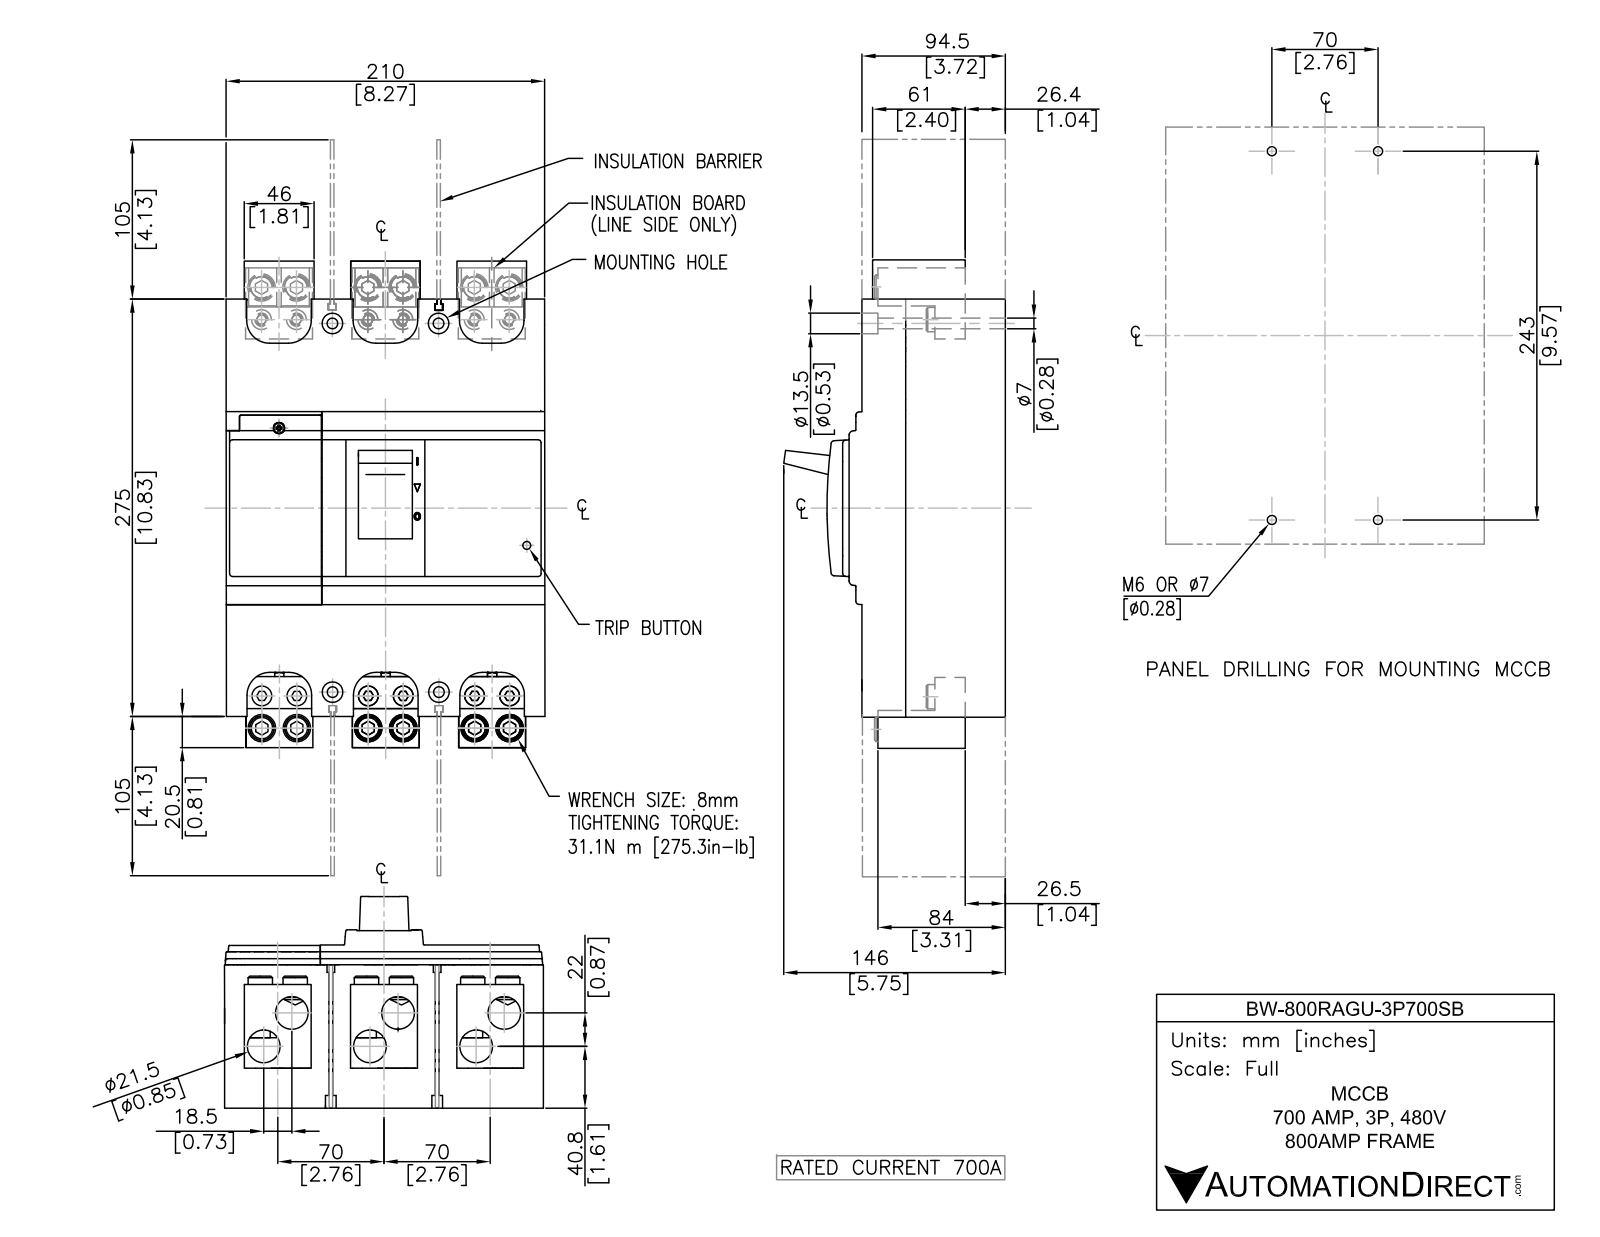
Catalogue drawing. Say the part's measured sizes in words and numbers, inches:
The part is named "BW800RAGU-3P700SB". Its 3-D file was written by "SolidWorks 2019 (CONFIG_CONTROL_DESIGN)". It is 32 solids with 717 faces: 403 planar, 194 cylindrical and 120 other. Overall it measures 12.795 by 8.268 by 5.819 inches. Its volume is 338.7 cubic inches and its surface area 638.4 square inches. Round holes: 12 of diameter 0.34, 12 of diameter 0.63, 12 of diameter 0.846, 6 of diameter 0.472, 4 of diameter 0.138, 4 of diameter 0.276, 4 of diameter 0.531, 1 of diameter 0.205. Round bosses or shafts: 12 of diameter 0.512, 12 of diameter 0.315, 2 of diameter 0.63. Partial cylindrical surfaces (rounded edges, fillets, slot ends): 12 of radius 0.591. The main face-to-face distances are 2.756, 8.268, 3.72, 1.732, 1.043, 2.677, 0.492, 3.169, 0.512, 4.213. The hole center spacings are 2.756, 5.512, 0.53, 1.378, 2.879, 2.889, 9.666, 9.853.
